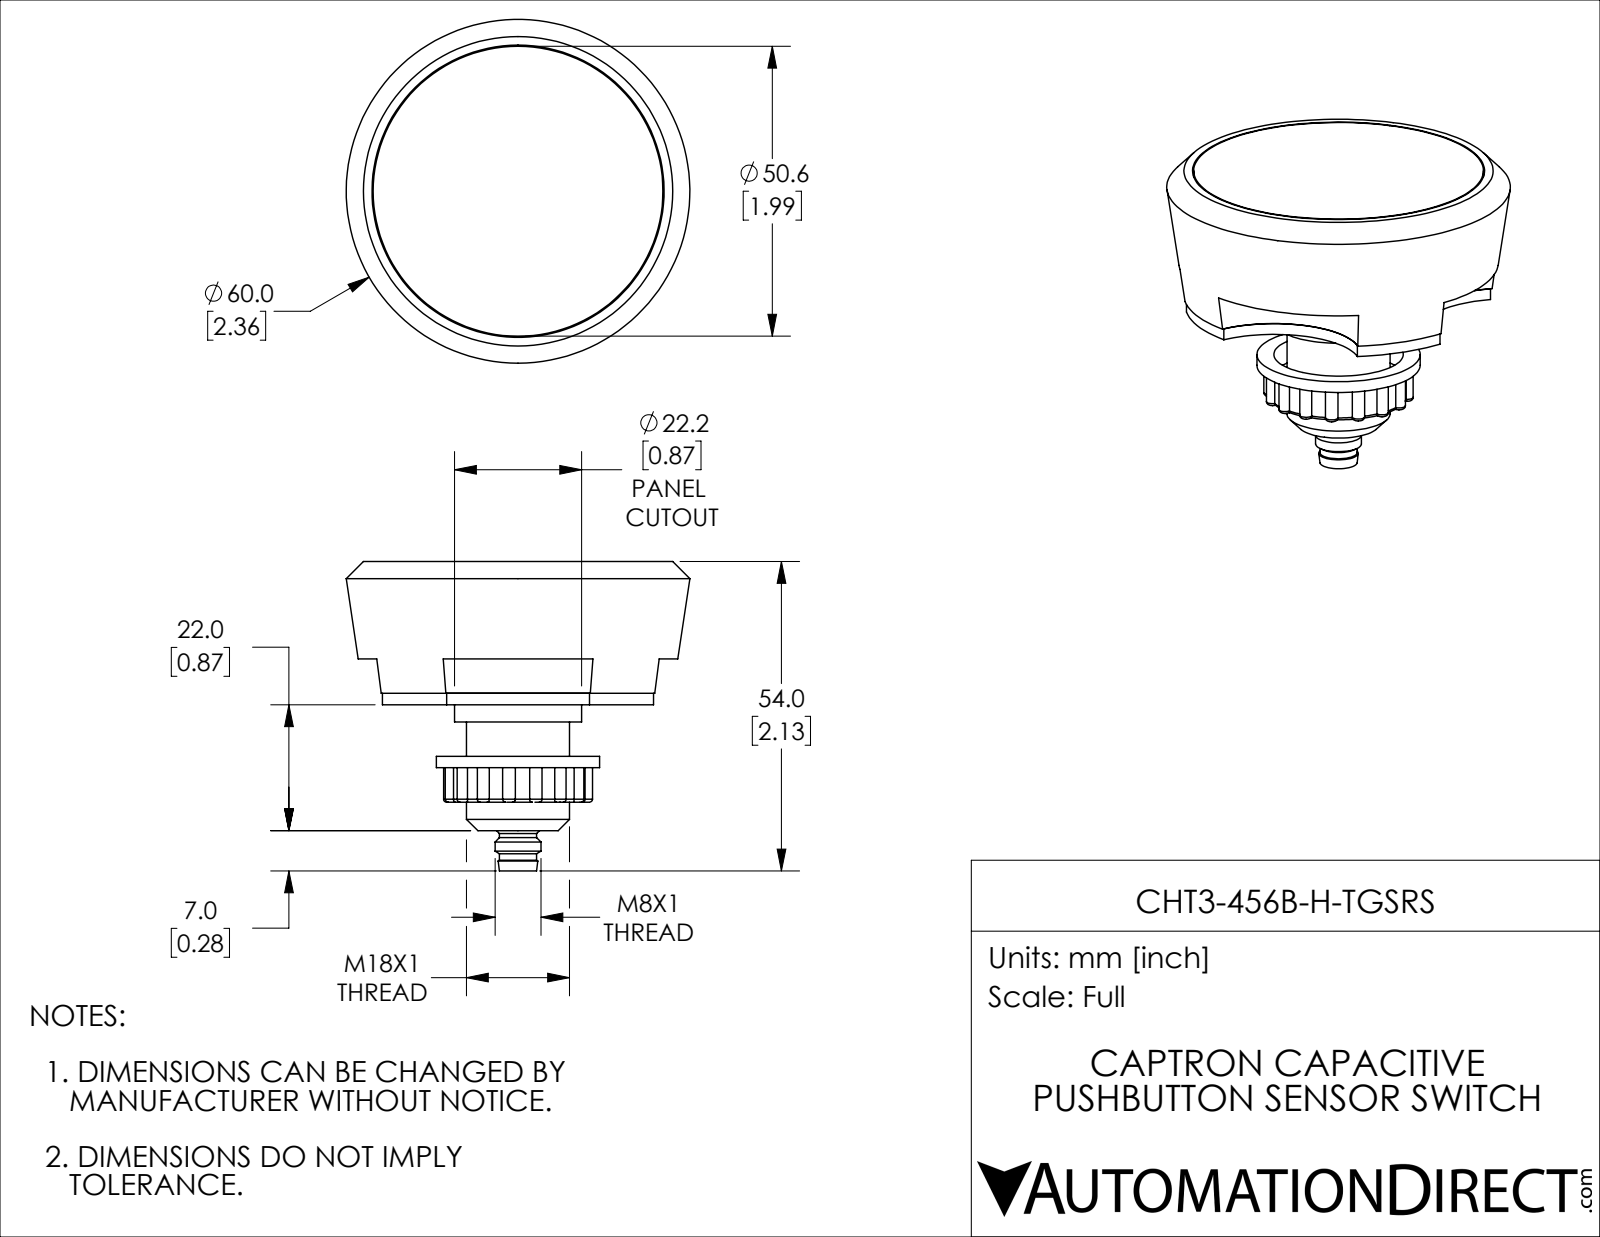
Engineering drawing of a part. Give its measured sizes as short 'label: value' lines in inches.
name: CHT3-456B-H-TGSRS
written by: SolidWorks 2019 (CONFIG_CONTROL_DESIGN)
unit: in
bodies: 10 solids, 200 faces (28 planar, 94 cylindrical, 78 other)
size: 2.362 × 2.362 × 2.126
volume: 3.853 in³; area: 32.45 in²
holes: 1× ⌀0.669, 1× ⌀0.89, 1× ⌀2.008
bosses: 5× ⌀0.039, 1× ⌀1.992, 1× ⌀1.122, 1× ⌀0.874, 1× ⌀0.709, 1× ⌀0.315, 1× ⌀0.256
rounds: 16× R0.043, 4× R0.591, 2× R0.02, 1× R0.039, 1× R0.114, 1× R0.472, 1× R1.053
face distances: 0.906, 0.091, 0.815, 0.134, 0.772, 0.043, 0.079, 0.984, 0.669, 0.85
